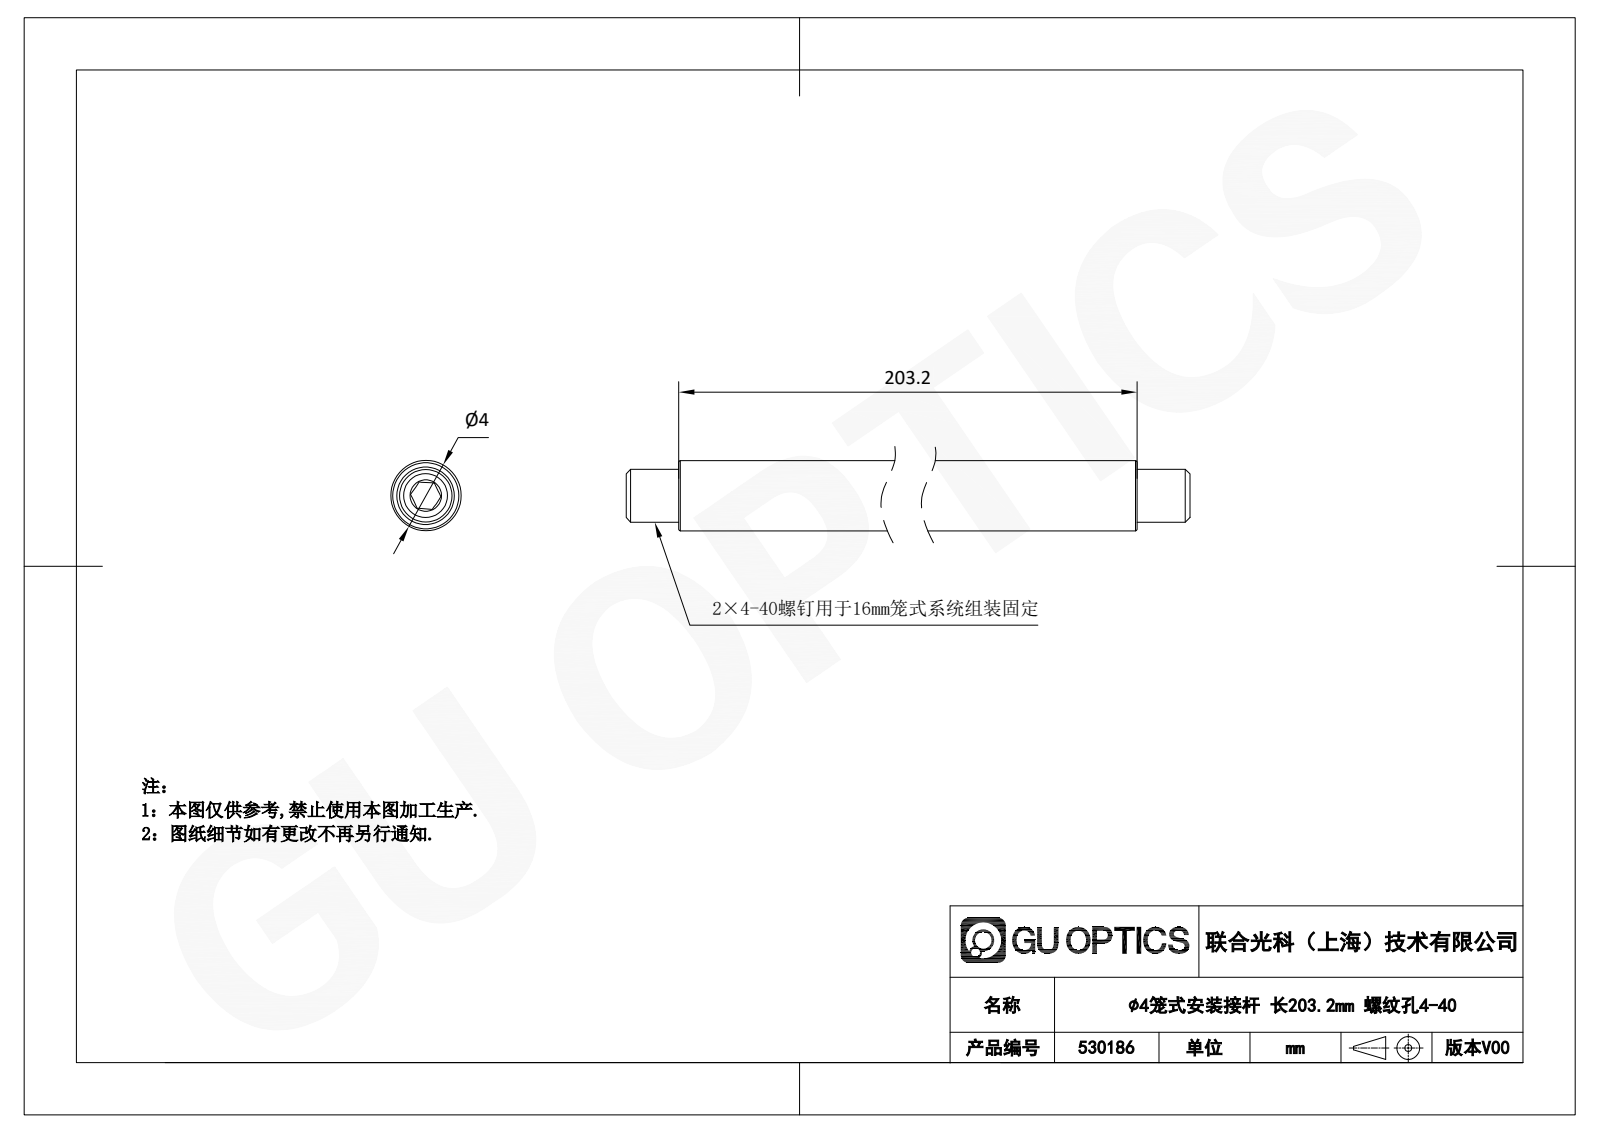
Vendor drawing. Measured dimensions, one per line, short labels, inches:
name: 530186
written by: SolidWorks 2020 (CONFIG_CONTROL_DESIGN)
unit: in
bodies: 3 solids, 37 faces (20 planar, 5 cylindrical, 12 other)
size: 8.394 × 0.157 × 0.157
volume: 0.159 in³; area: 4.407 in²
holes: 1× ⌀0.098
bosses: 1× ⌀0.157, 1× ⌀0.118
face distances: 0.118, 7.882, 0.197, 0.315, 8.079, 8.197, 0.059, 8, 0.039, 8.354
